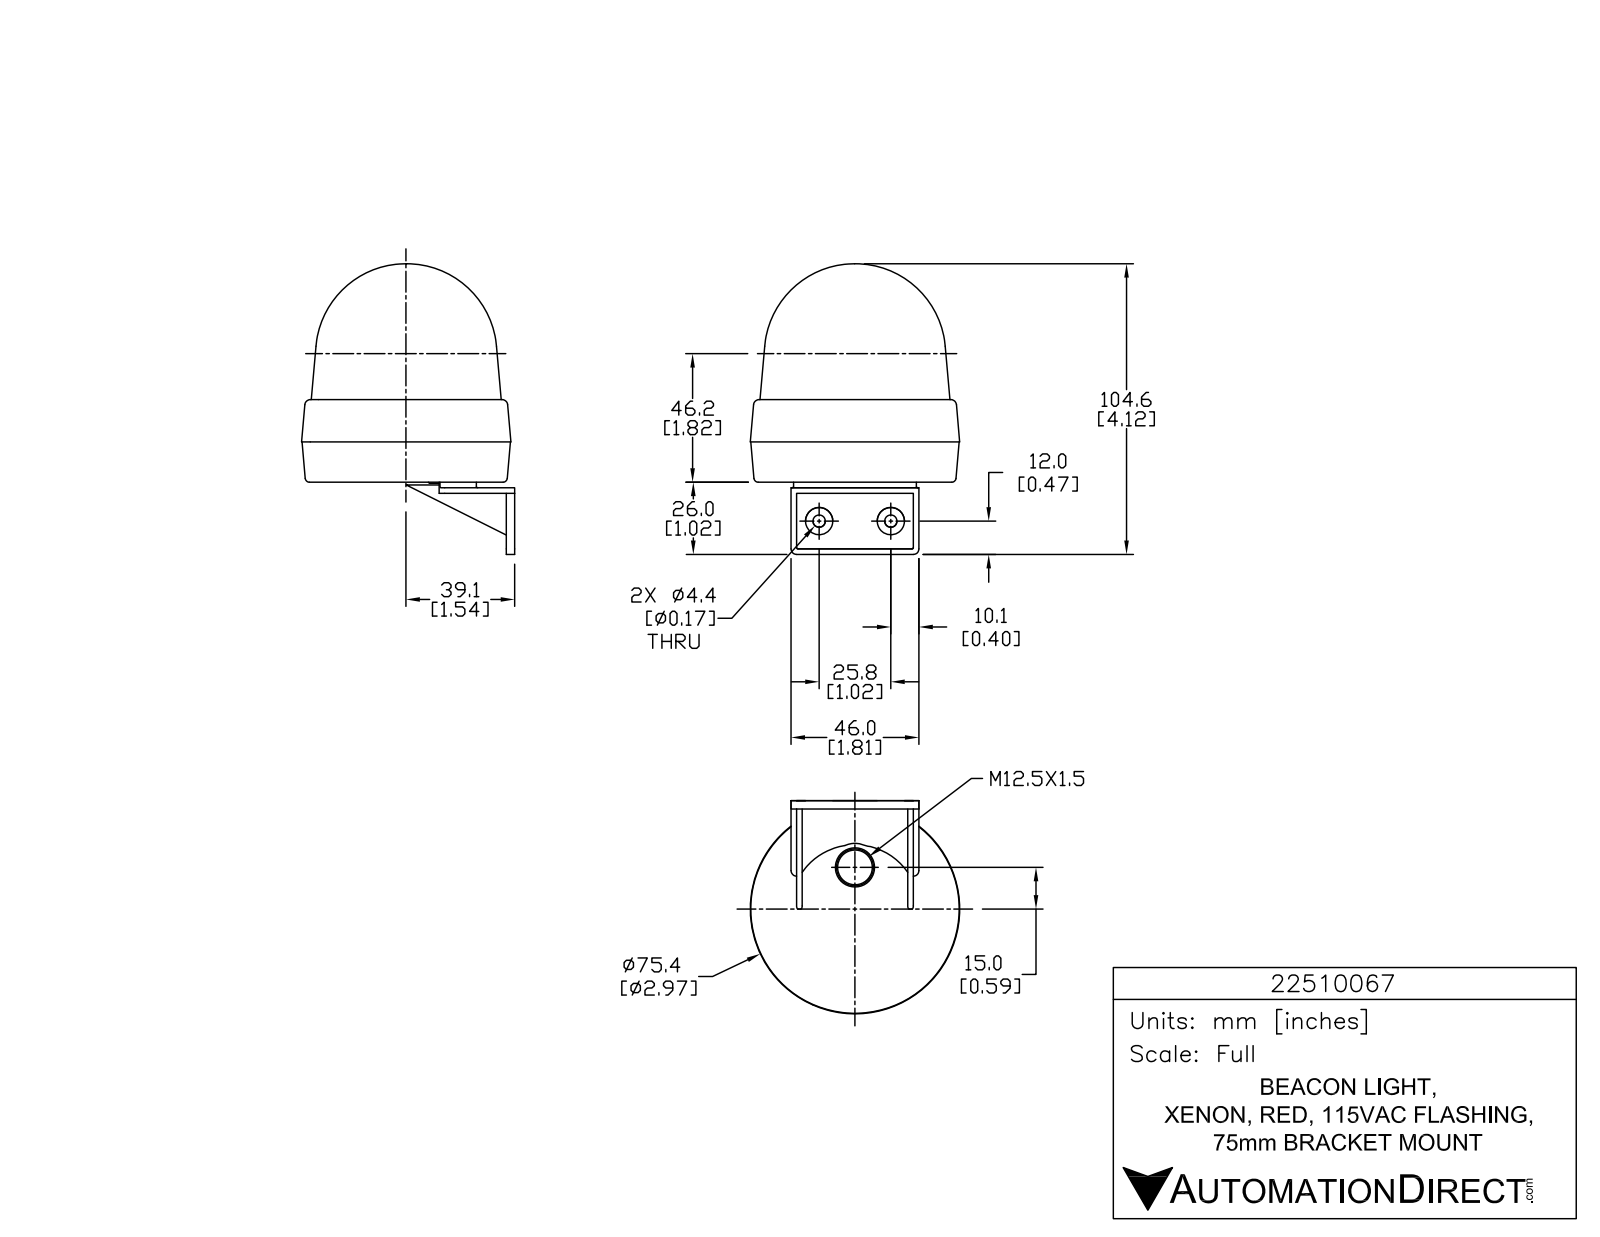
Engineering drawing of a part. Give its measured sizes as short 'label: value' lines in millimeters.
name: 22510067
written by: SolidWorks 2015 (AUTOMOTIVE_DESIGN)
unit: mm
bodies: 1 solid, 819 faces (549 planar, 180 cylindrical, 90 other)
size: 104.6 × 82.6 × 75.4
volume: 262 500 mm³; area: 27 080 mm²
holes: 3× ⌀1.5, 2× ⌀4.4
bosses: 3× ⌀8.6, 3× ⌀2.1, 2× ⌀9.8
rounds: 9× R0.1, 6× R0.1, 6× R0.3, 6× R0.3, 6× R0.3, 6× R0.5, 6× R5, 4× R2
face distances: 2, 4, 40, 1, 3, 42, 38, 2, 42, 44
hole spacings: 25.8
